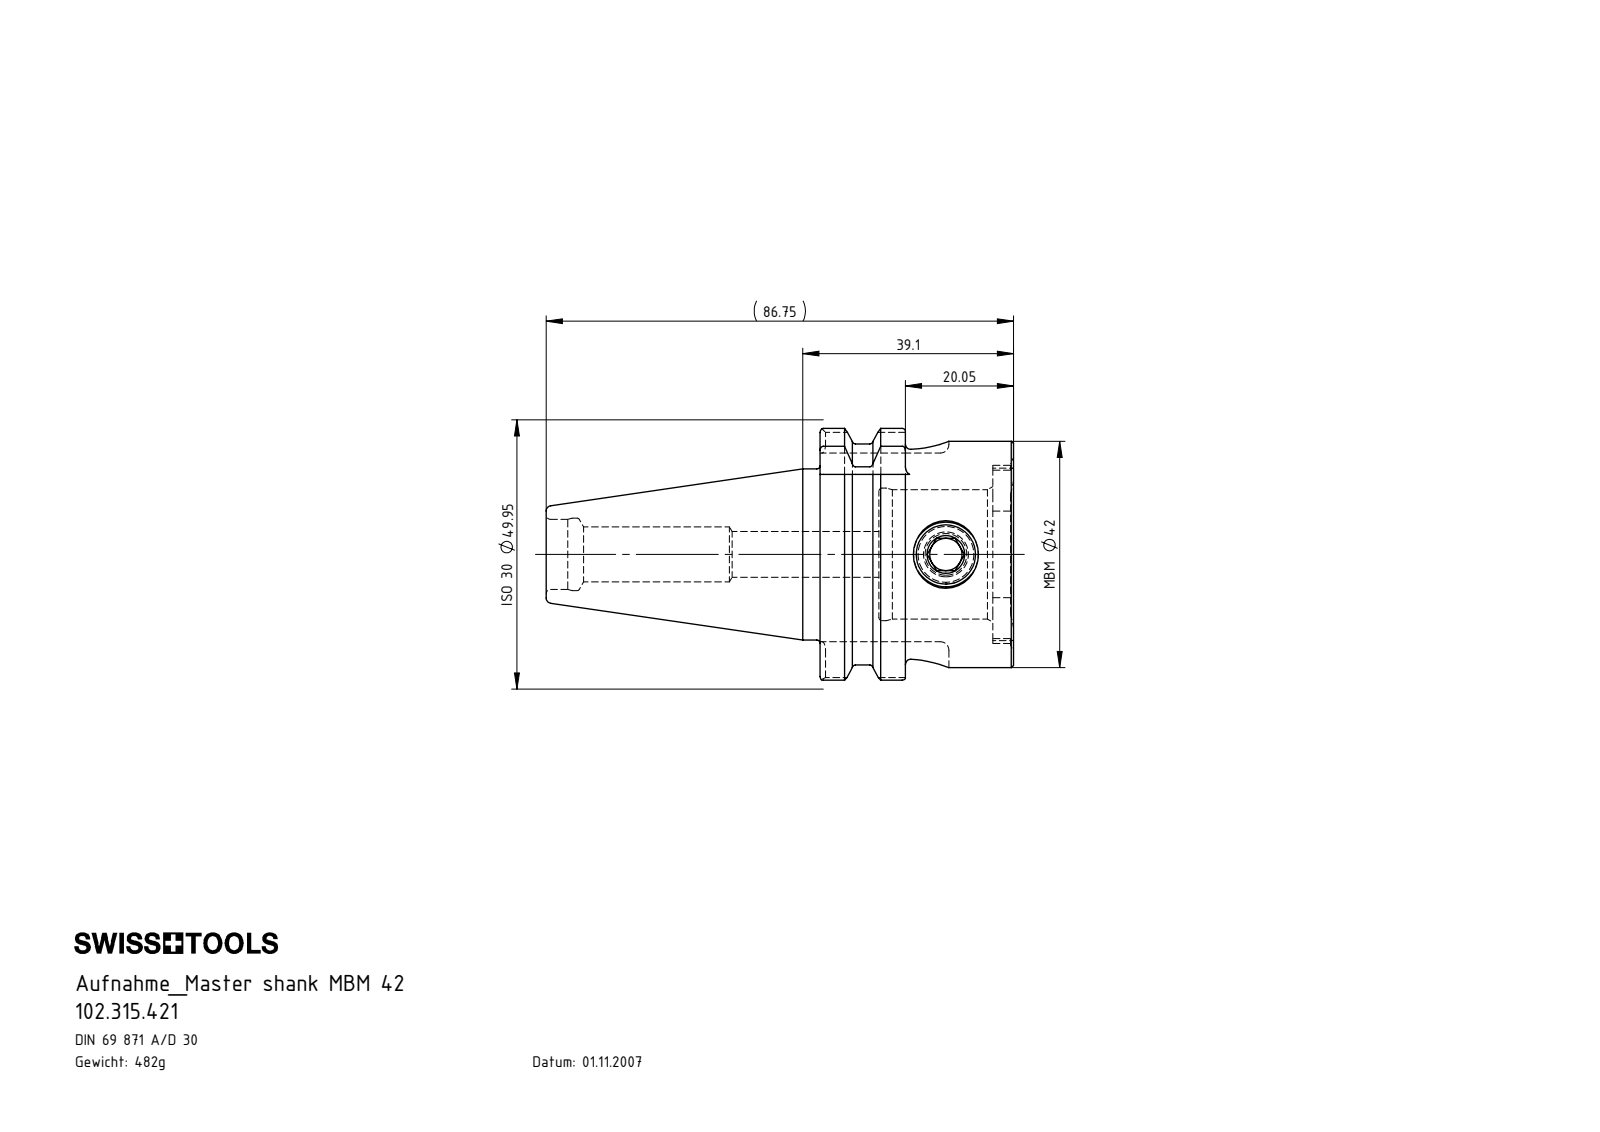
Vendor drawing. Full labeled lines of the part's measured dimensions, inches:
Part name (STEP PRODUCT): MB4-ER1.001.013_A; SK3-MB4.K01.039_C; 102.315.421
STEP written by: SolidWorks 2017 (CONFIG_CONTROL_DESIGN)
Units: inches
Bodies: 2 solids, 177 faces (51 planar, 56 cylindrical, 70 other)
Overall size (bounding box): 3.415 × 1.967 × 1.838
Volume: 3.746 in³ · Surface area: 26.67 in²
Round holes (diameter × count): ⌀0.236 ×1, ⌀0.335 ×1, ⌀0.402 ×1, ⌀0.433 ×1, ⌀0.512 ×1, ⌀0.53 ×1, ⌀0.945 ×1, ⌀0.969 ×1
Round bosses / shafts (diameter × count): ⌀1.654 ×1, ⌀1.25 ×1, ⌀0.472 ×1
Partial cylindrical surfaces — rounded edges, fillets, slot ends (radius × count): R0.063 ×8, R0.205 ×4, R0.315 ×1, R0.317 ×1, R0.587 ×1, R0.65 ×1, R0.867 ×1, R0.983 ×1
Main face-to-face distances: 0.429, 1.262, 0.833, 1.413, 0.984, 0.152, 1.378, 0.624, 0.195, 0.638
